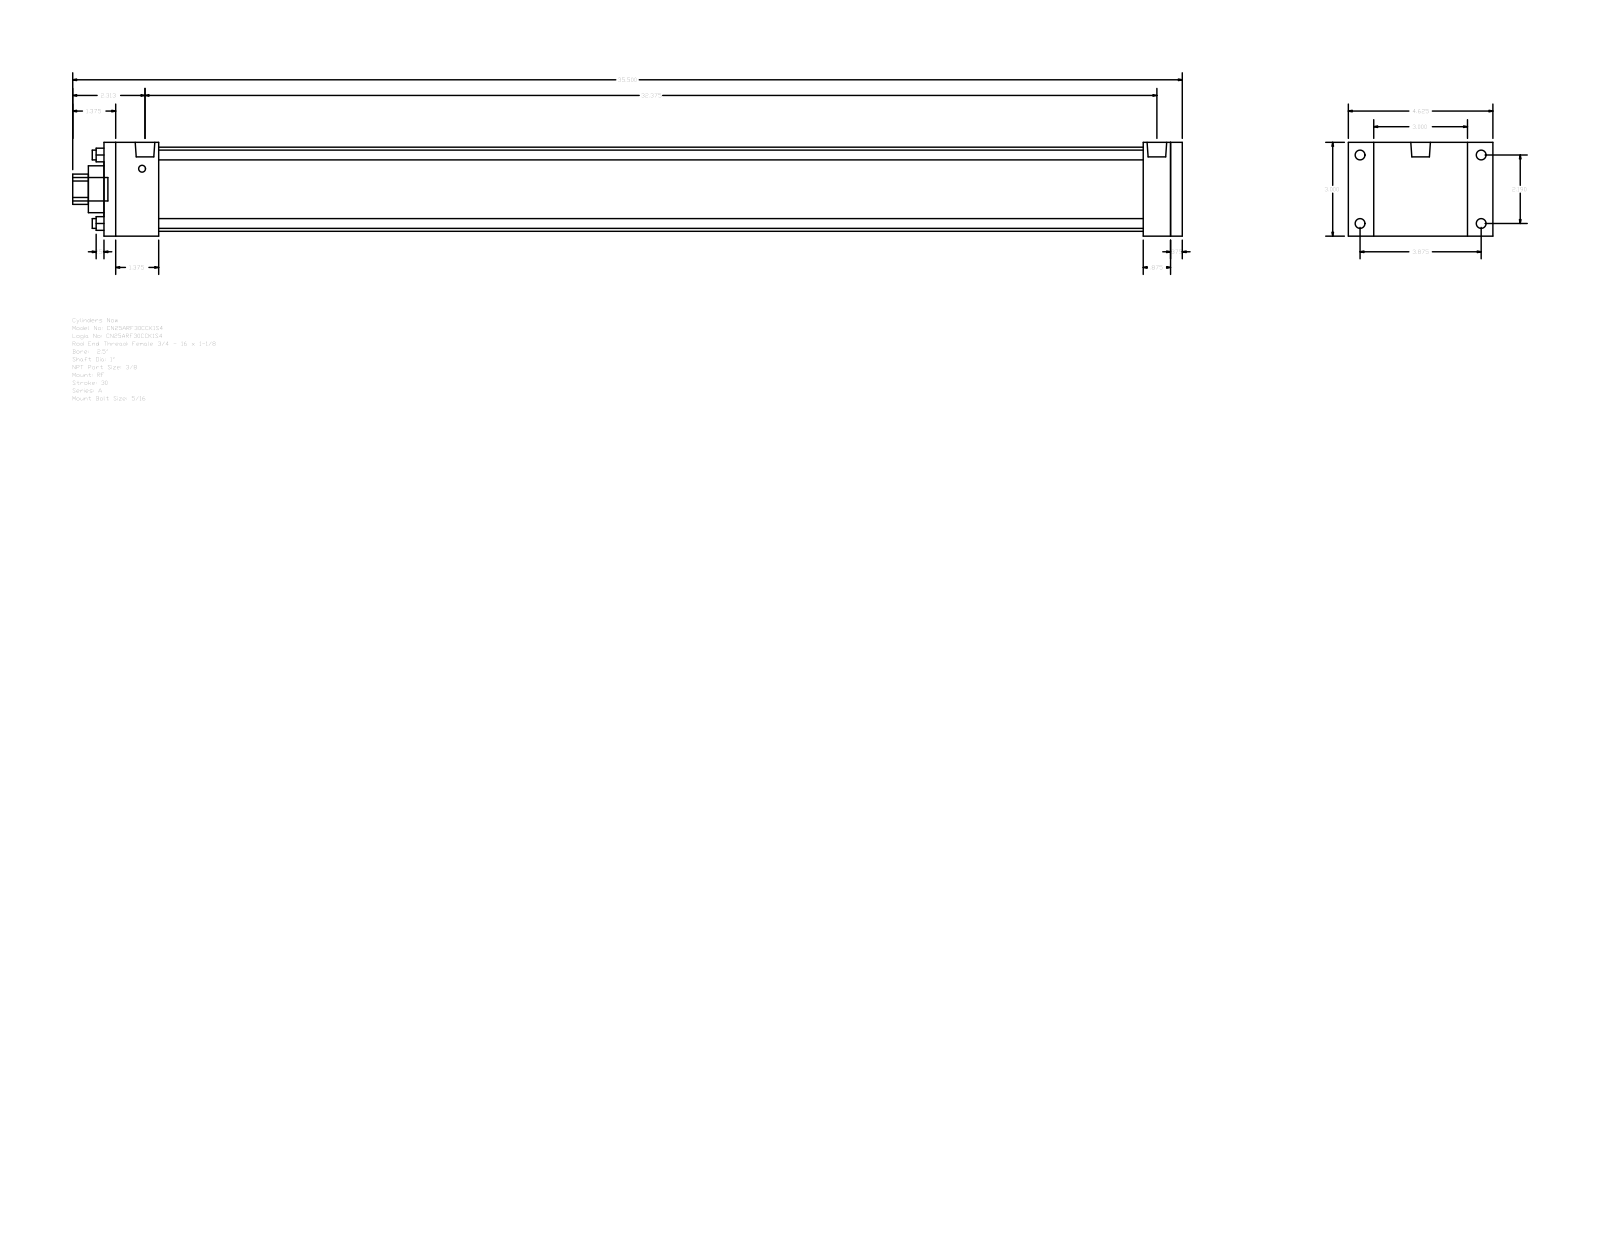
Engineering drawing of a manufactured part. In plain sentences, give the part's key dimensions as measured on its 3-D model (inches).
The part is named "A_RF__0250_1". Its 3-D file was written by "GSSL Pune (CONFIG_CONTROL_DESIGN)". It is 0 solids with 92 faces: 64 planar, 28 cylindrical and 0 other. Overall it measures 35.5 by 4.625 by 3 inches. Round holes: 4 of diameter 0.313, 1 of diameter 1, 1 of diameter 1.5, 1 of diameter 2.69. Round bosses or shafts: 4 of diameter 0.313, 4 of diameter 0.219, 2 of diameter 0.627, 1 of diameter 0.75. Partial cylindrical surfaces (rounded edges, fillets, slot ends): 1 of radius 0.484. The main face-to-face distances are 3, 34.5, 0.375, 34.125, 1.75, 33.25, 31.5, 32.375, 32.75, 0.875. The hole center spacings are 1.548, 2.19, 3.097.
